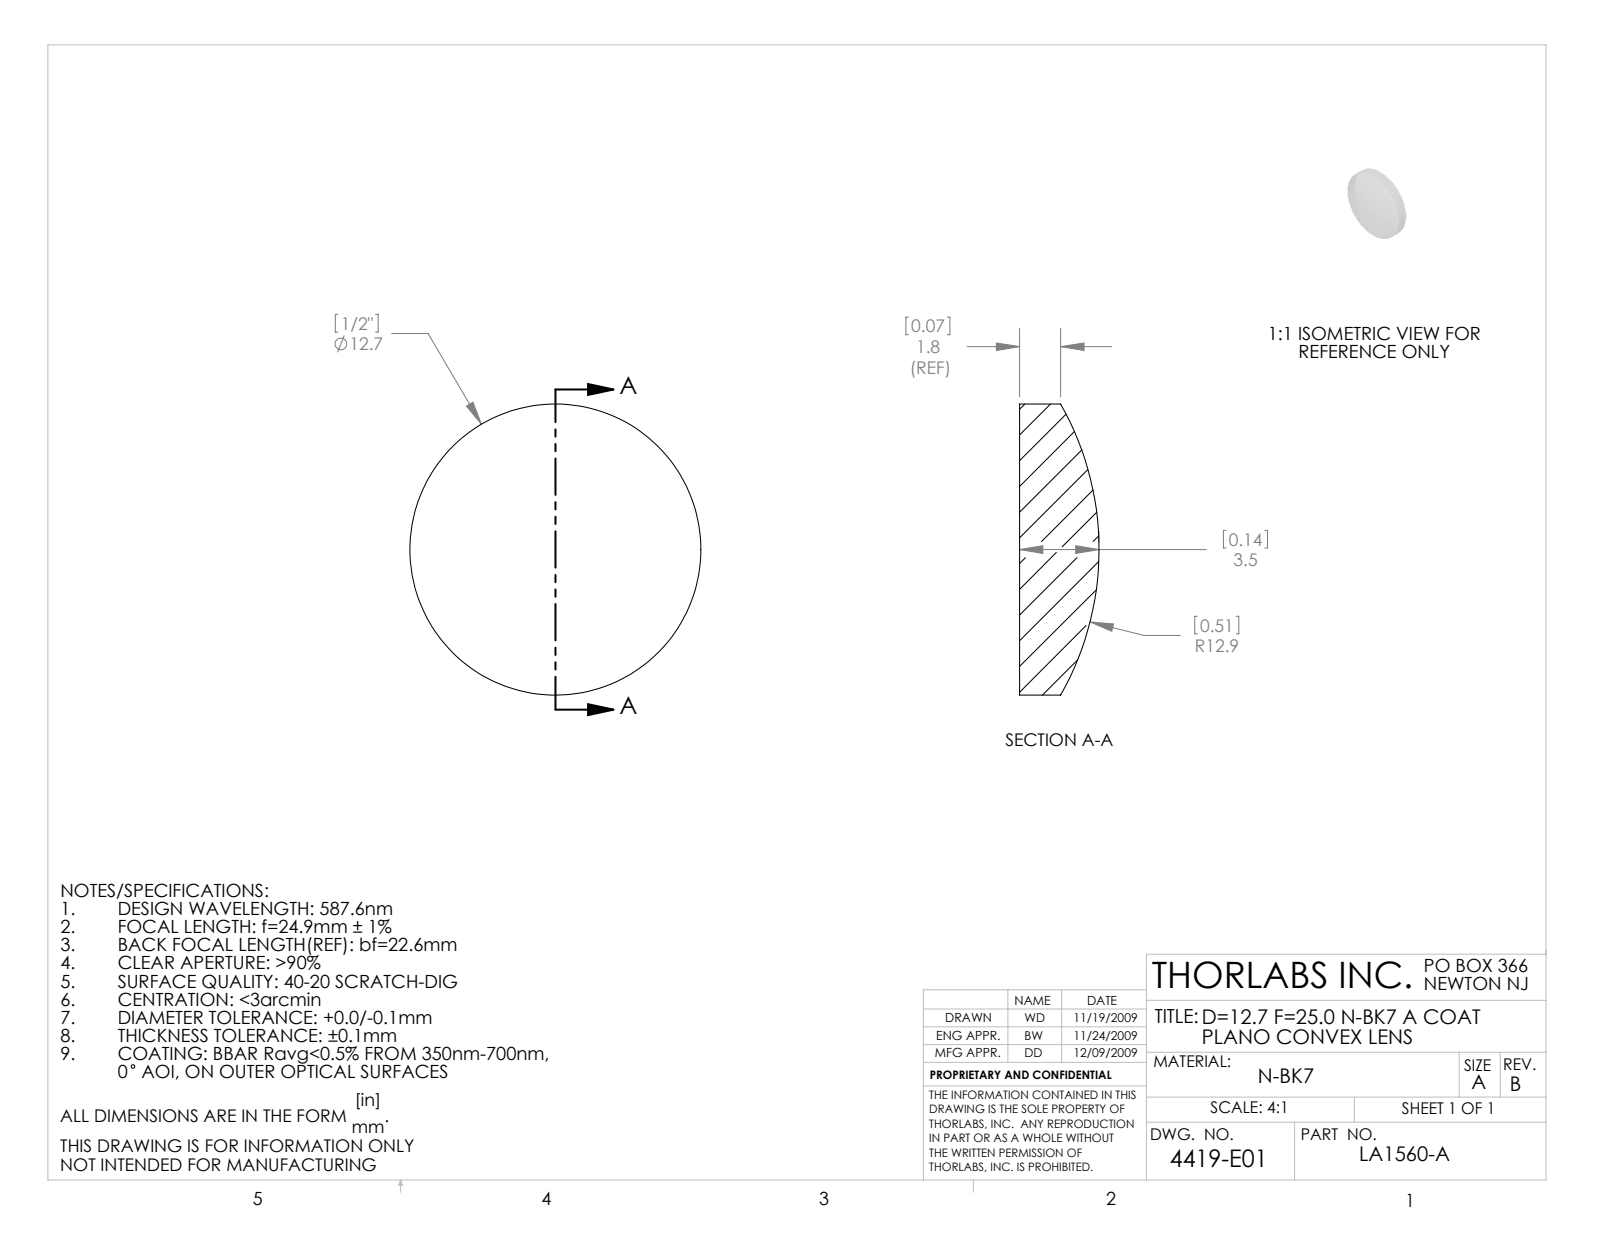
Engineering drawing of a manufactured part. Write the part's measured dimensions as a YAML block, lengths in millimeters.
part_name: "4419-E0W"
step_written_by: "SolidWorks 2009 (AUTOMOTIVE_DESIGN)"
units: millimeters
bodies: {solids: 1, faces: 5, planar: 1, cylindrical: 2, other: 2}
overall_size: [12.7, 12.7, 3.47]
volume: 336
surface_area: 334
round_bosses_or_shafts:
  - {diameter: 12.7, count: 1}
